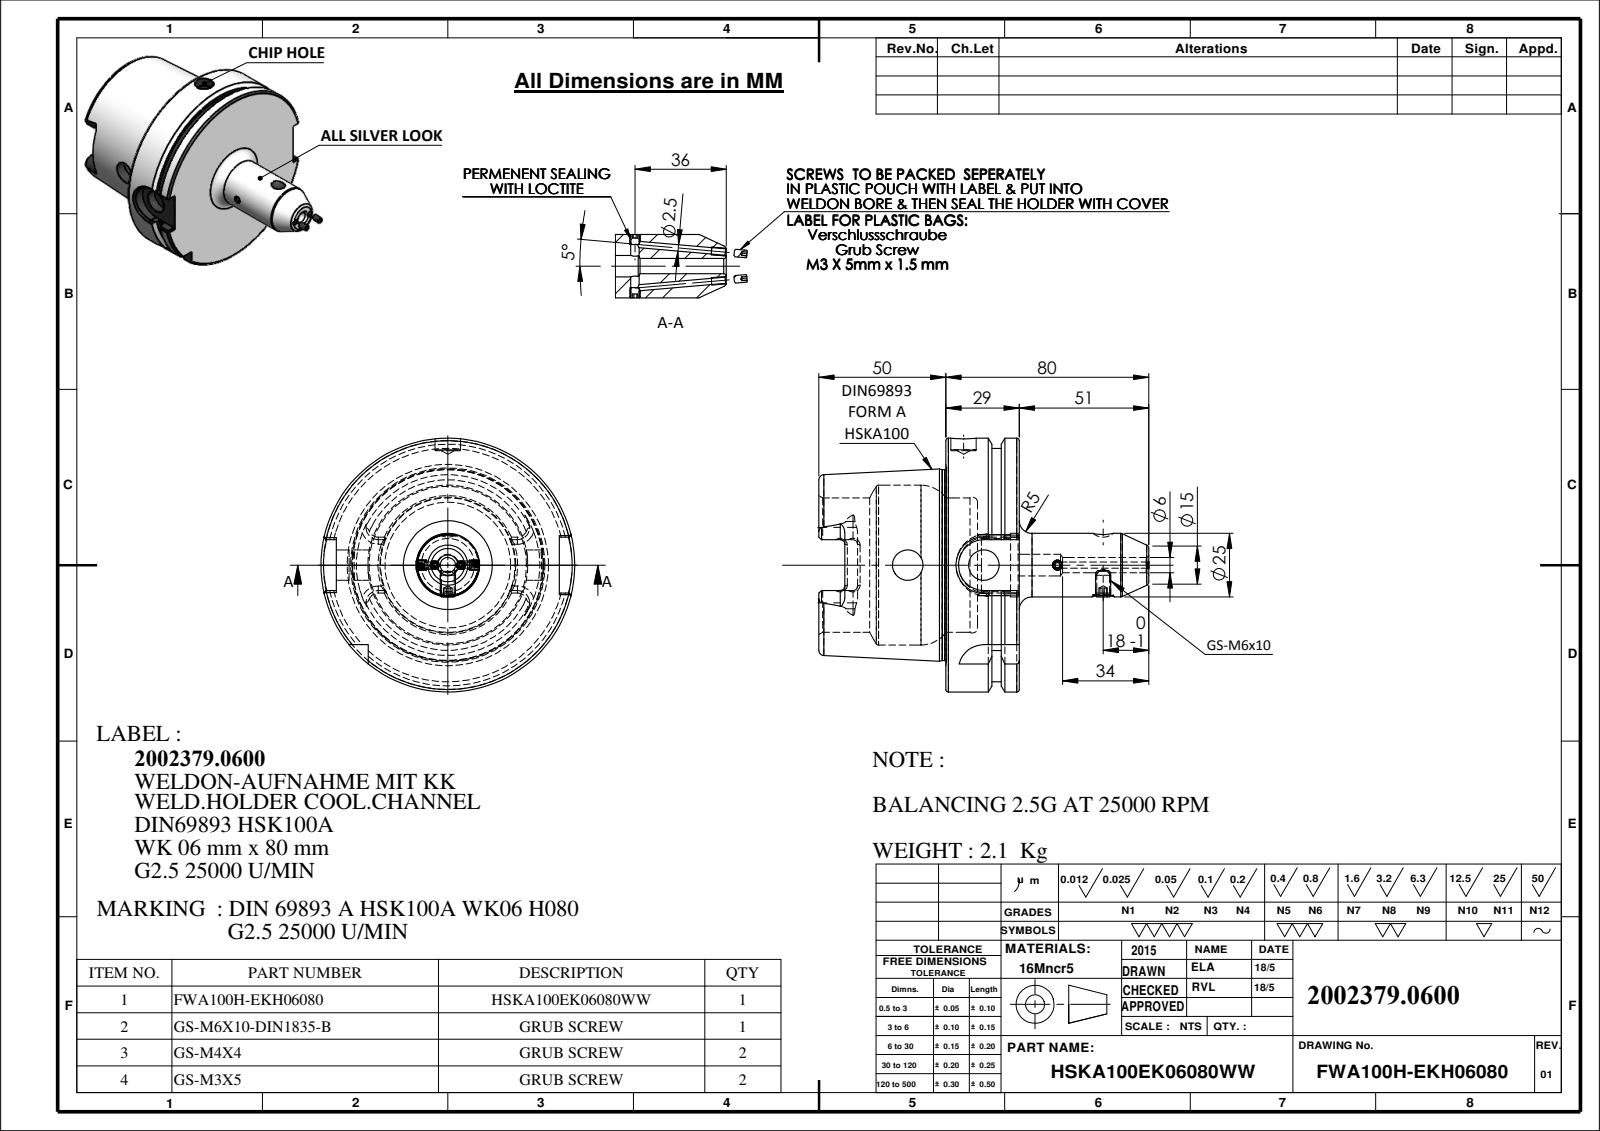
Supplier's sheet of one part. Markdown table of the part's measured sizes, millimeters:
| quantity | value |
| --- | --- |
| part name | HSKA100EK06080WW-R02; GS-M4X4_DIN 913 - M4 x 4-N; GS-M3X5; 91100A-WK06080 (+2 more) |
| STEP written by | SolidWorks 2018 (CONFIG_CONTROL_DESIGN) |
| units | millimeters |
| bodies | 6 solids, 356 faces (110 planar, 88 cylindrical, 158 other) |
| overall size | 138.21 × 100 × 100 |
| volume | 275 095 mm³ |
| surface area | 55 677 mm² |
| round holes (diameter × count) | 2.5 × 2, 12 × 2, 3.3 × 1, 5 × 1, 6 × 1, 8 × 1, 8.5 × 1, 10 × 1, 21 × 1, 25 × 1, 53 × 1, 63 × 1 |
| round bosses / shafts (diameter × count) | 3 × 2, 100 × 1, 92 × 1, 75.16 × 1, 6 × 1, 4 × 1 |
| partial cylindrical surfaces (radius × count) | 1.8 × 6, 4.88 × 4, 10 × 2, 11 × 1 |
| main face-to-face distances | 28.95, 12.5, 16.45, 50, 62.5, 78.95, 78.5, 28.5, 16, 0.45 |
| hole center spacings | 29, 30, 55, 59 |
